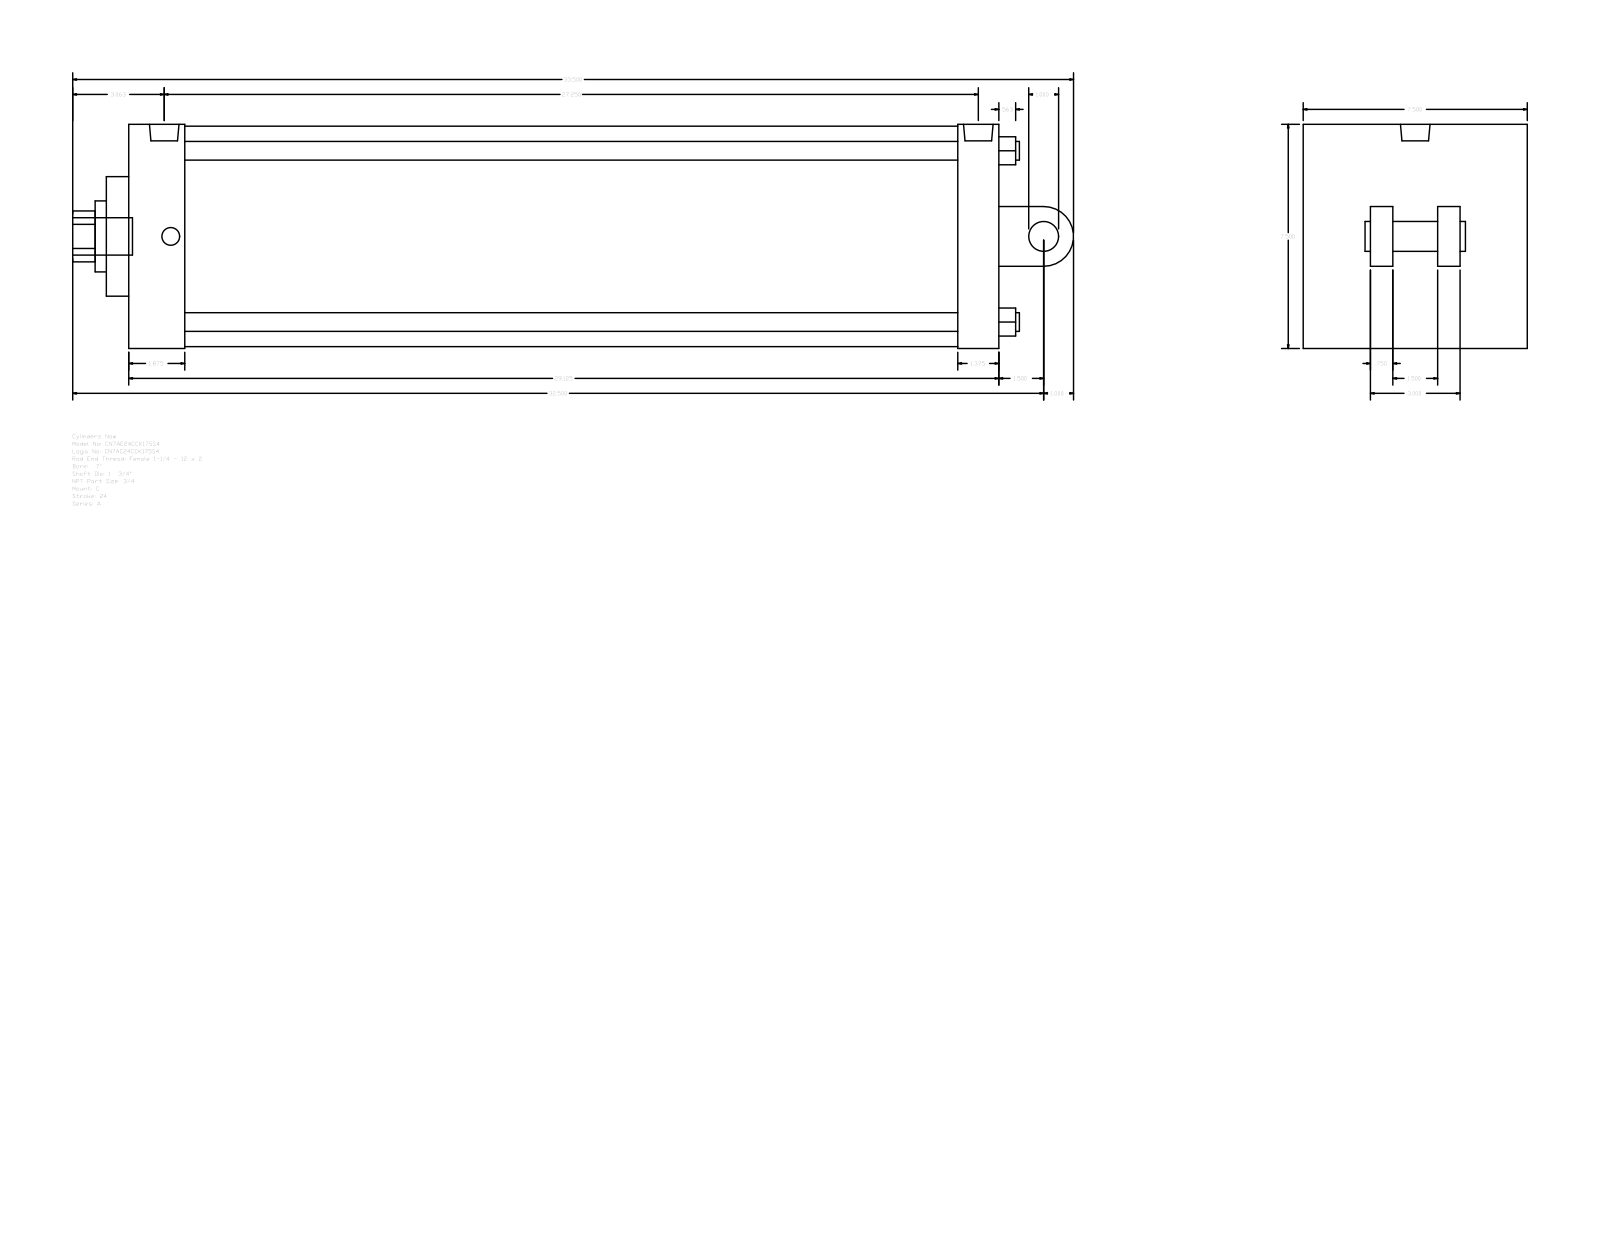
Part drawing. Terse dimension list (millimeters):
name: A_C__0700_1.75
written by: GSSL Pune (CONFIG_CONTROL_DESIGN)
unit: mm
bodies: 0 solids, 104 faces (75 planar, 29 cylindrical, 0 other)
size: 850.9 × 190.5 × 190.5
holes: 4× ⌀15.88, 2× ⌀15.08, 1× ⌀25.12, 1× ⌀44.45, 1× ⌀60.33, 1× ⌀187.32
bosses: 2× ⌀15.08, 1× ⌀31.75, 1× ⌀25.4, 1× ⌀25.12
rounds: 1× R21.63, 1× R25.4
face distances: 190.5, 739.78, 19.05, 76.2, 57.15, 44.45, 34.92, 47.63, 692.15, 704.86
hole spacings: 102.91, 145.54, 205.82, 5.56
